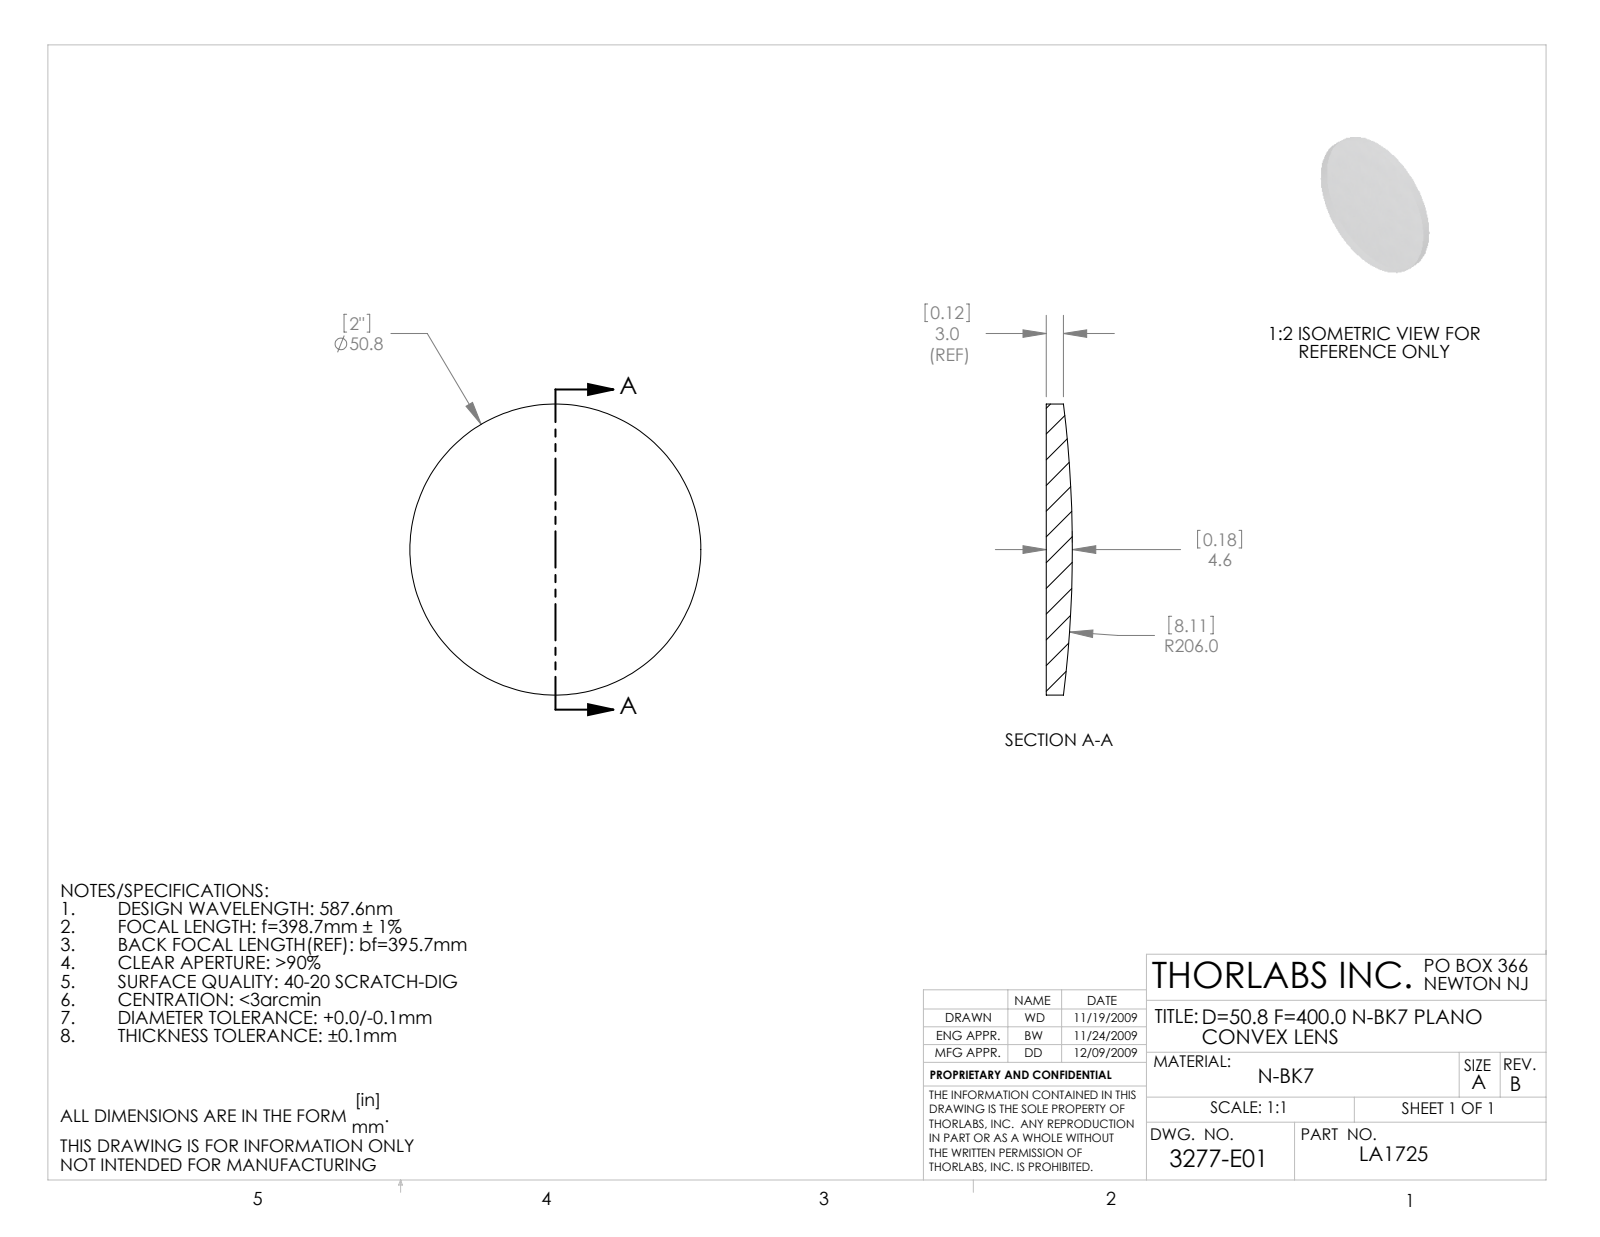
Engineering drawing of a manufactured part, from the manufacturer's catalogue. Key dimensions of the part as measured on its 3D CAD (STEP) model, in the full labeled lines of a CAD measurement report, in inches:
Part name (STEP PRODUCT): 3277-E0W
STEP written by: SolidWorks 2009 (AUTOMOTIVE_DESIGN)
Units: inches
Bodies: 1 solid, 5 faces (1 planar, 2 cylindrical, 2 other)
Overall size (bounding box): 2 × 2 × 0.18
Volume: 0.468 in³ · Surface area: 7.037 in²
Round bosses / shafts (diameter × count): ⌀2 ×1
